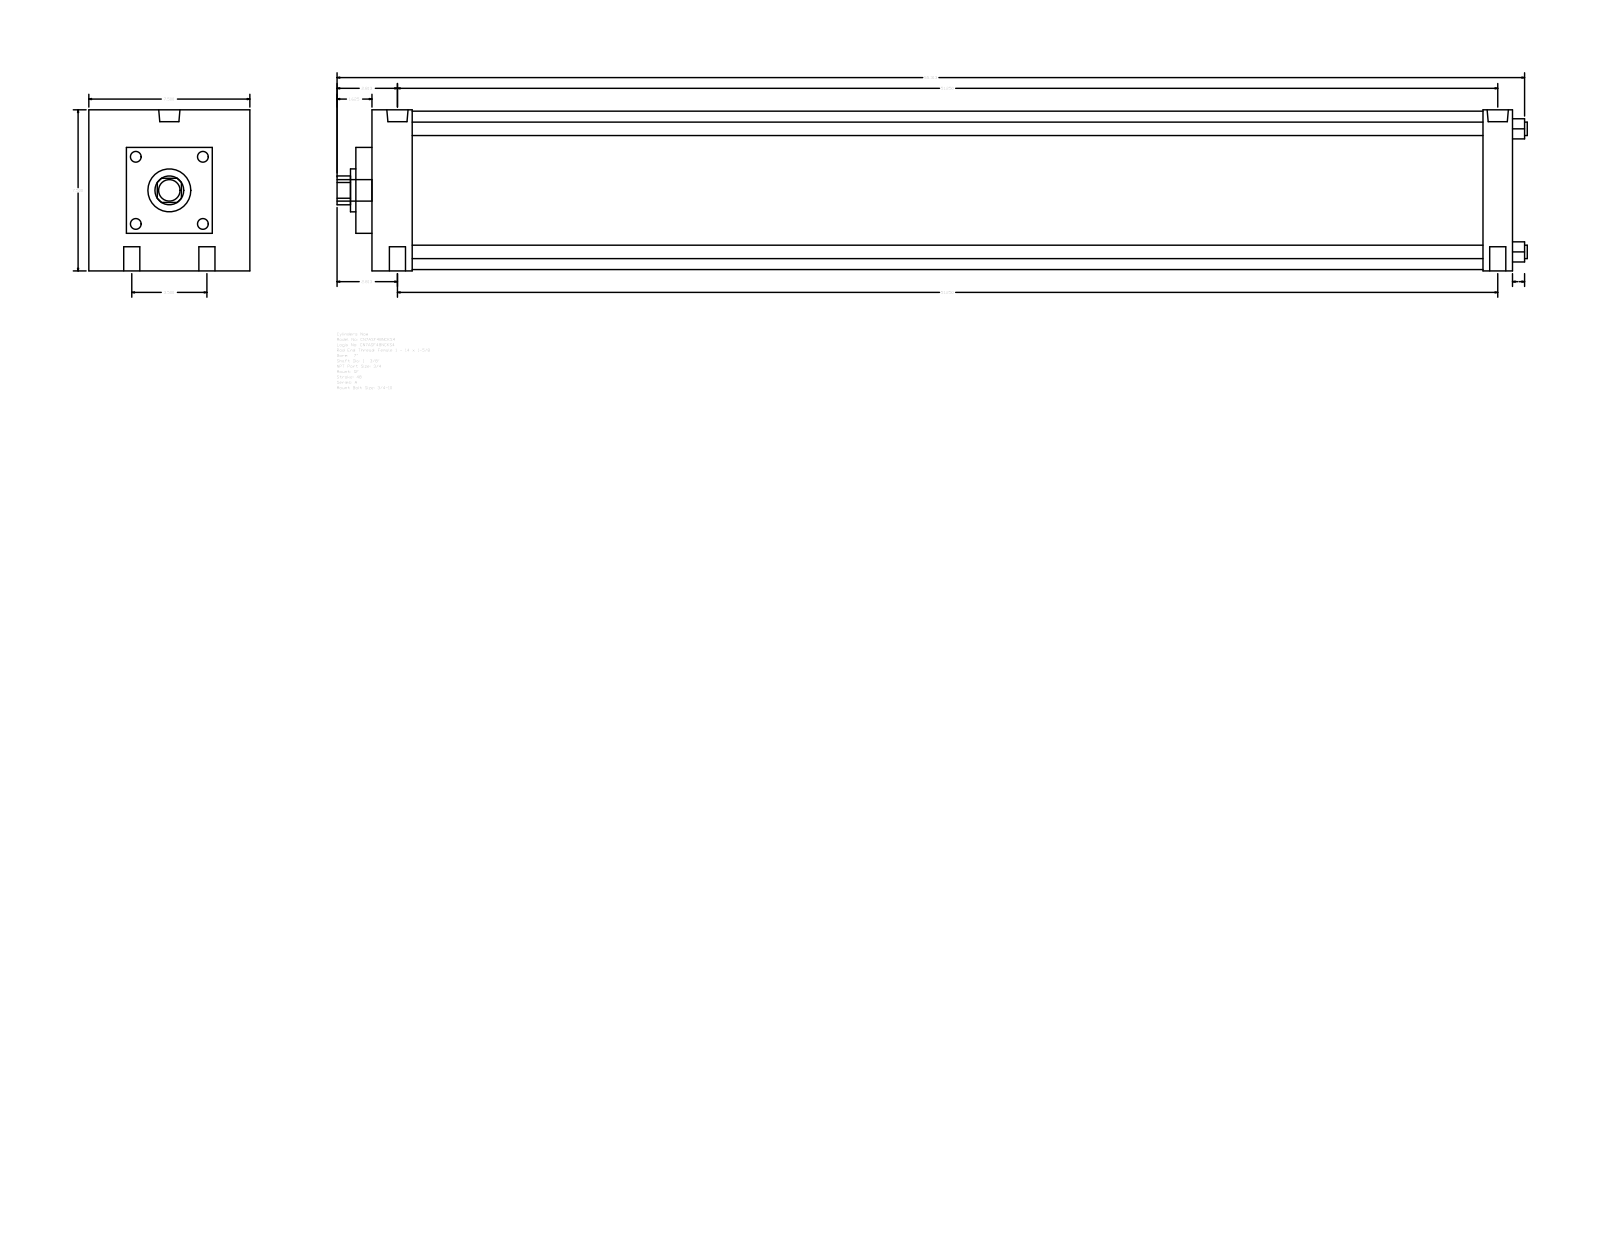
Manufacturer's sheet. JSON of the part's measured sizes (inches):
{"part_name": "A_SF__0700_1.375", "step_written_by": "GSSL Pune (CONFIG_CONTROL_DESIGN)", "units": "inches", "bodies": {"solids": 0, "faces": 93, "planar": 67, "cylindrical": 26, "other": 0}, "overall_size": [55.437, 7.5, 7.5], "round_holes": [[0.75, 4], [0.594, 2], [0.989, 2], [1.375, 1], [2, 1]], "round_bosses_or_shafts": [[0.625, 4], [7.375, 1], [1, 1]], "partial_cylinders_radius": [[0.672, 1]], "face_to_face_distances": [7.5, 53.125, 0.75, 53.875, 2.625, 52.5, 1.875, 51.75, 49.875, 51.25], "hole_center_spacings": [1.75, 51.28, 51.25, 3.5, 51.369, 50.812]}
